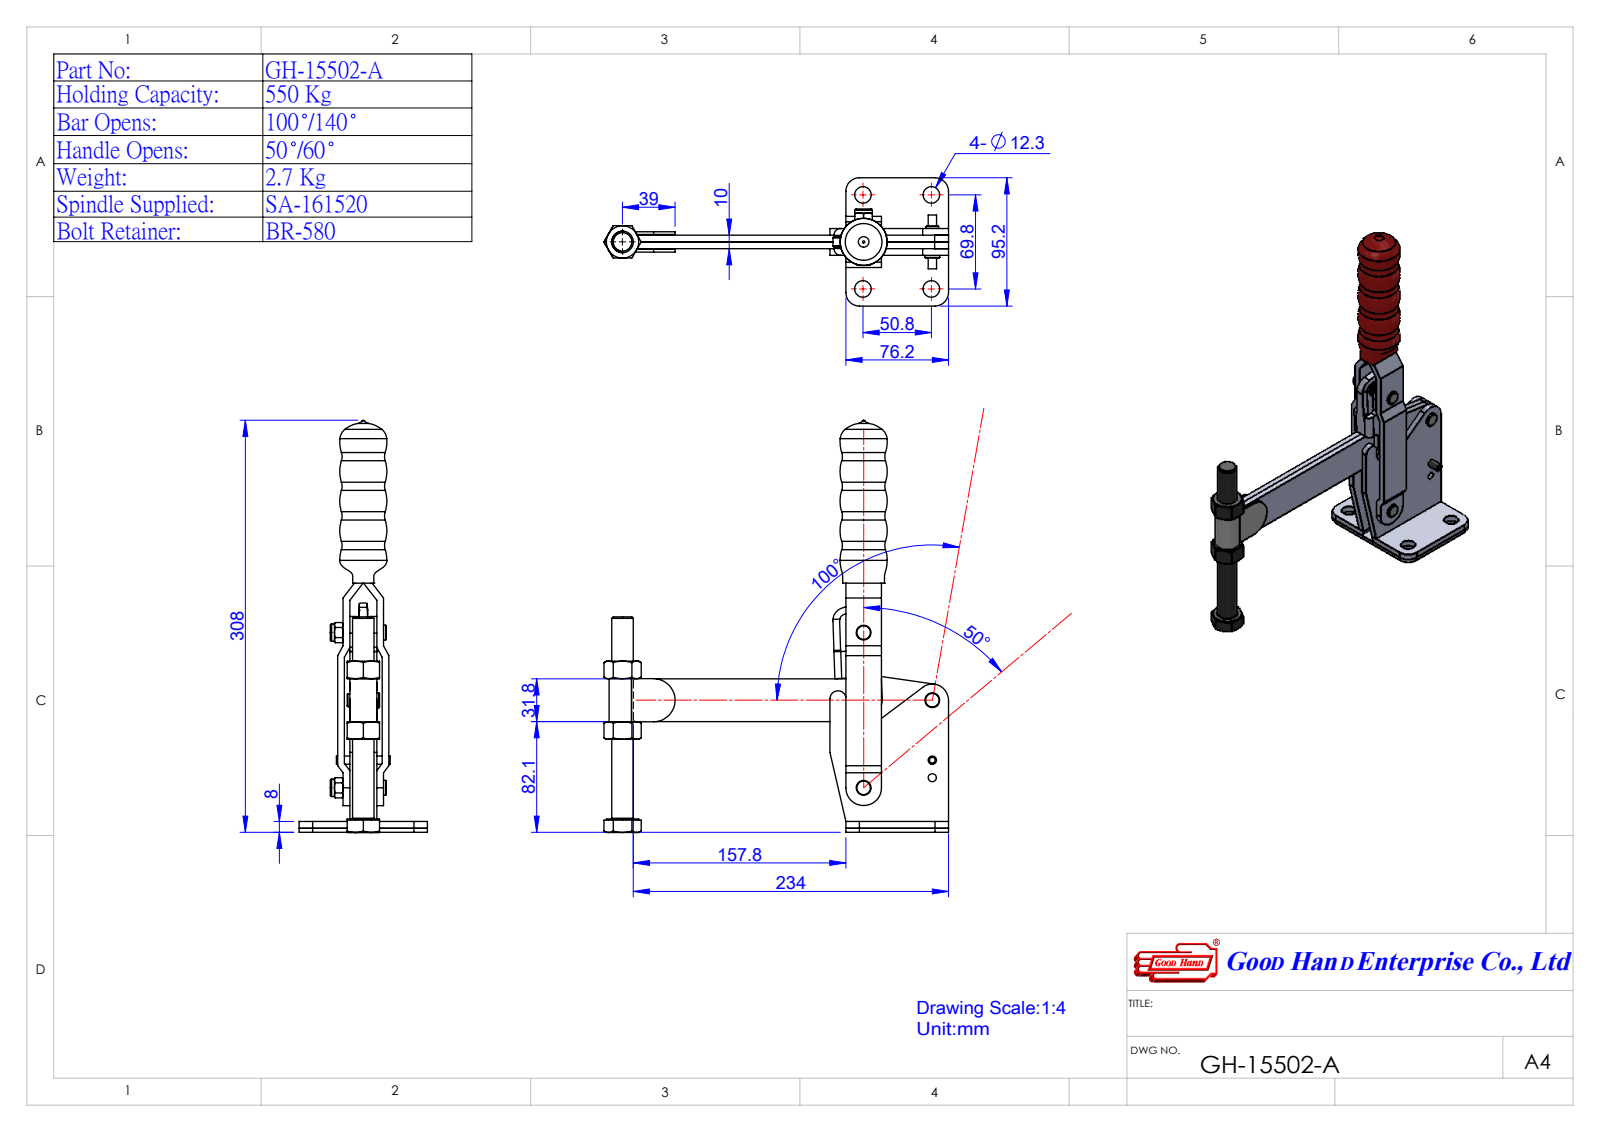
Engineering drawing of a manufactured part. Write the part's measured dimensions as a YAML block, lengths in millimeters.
part_name: "GH-15502-A(簡化)-1; Group2^GH-15502-A(簡化)-1; Group1^GH-15502-A(簡化)-1; Group6^GH-15502-A(簡化)-1 (+3 more)"
step_written_by: "SolidWorks 2016 (AUTOMOTIVE_DESIGN)"
units: millimeters
bodies: {solids: 6, faces: 365, planar: 144, cylindrical: 111, other: 110}
overall_size: [305.8, 289.95, 95.2]
volume: 415561
surface_area: 136495
round_holes:
  - {diameter: 7.5, count: 4}
  - {diameter: 12.3, count: 4}
  - {diameter: 6, count: 1}
  - {diameter: 14, count: 1}
  - {diameter: 16, count: 1}
round_bosses_or_shafts:
  - {diameter: 10, count: 2}
  - {diameter: 9.5, count: 2}
  - {diameter: 9.45, count: 2}
  - {diameter: 24, count: 1}
  - {diameter: 6, count: 1}
partial_cylinders:
  - {radius: 10, count: 4}
  - {radius: 12, count: 3}
  - {radius: 3, count: 2}
  - {radius: 3.01, count: 2}
  - {radius: 11, count: 2}
  - {radius: 6, count: 1}
  - {radius: 8.25, count: 1}
  - {radius: 11.25, count: 1}
face_to_face_distances: [5, 15, 10, 20, 24, 9, 4, 29, 8, 14]
hole_center_spacings: [50.8, 69.8, 86.33, 215.44, 265.69, 49.25, 50.23, 51.55]
